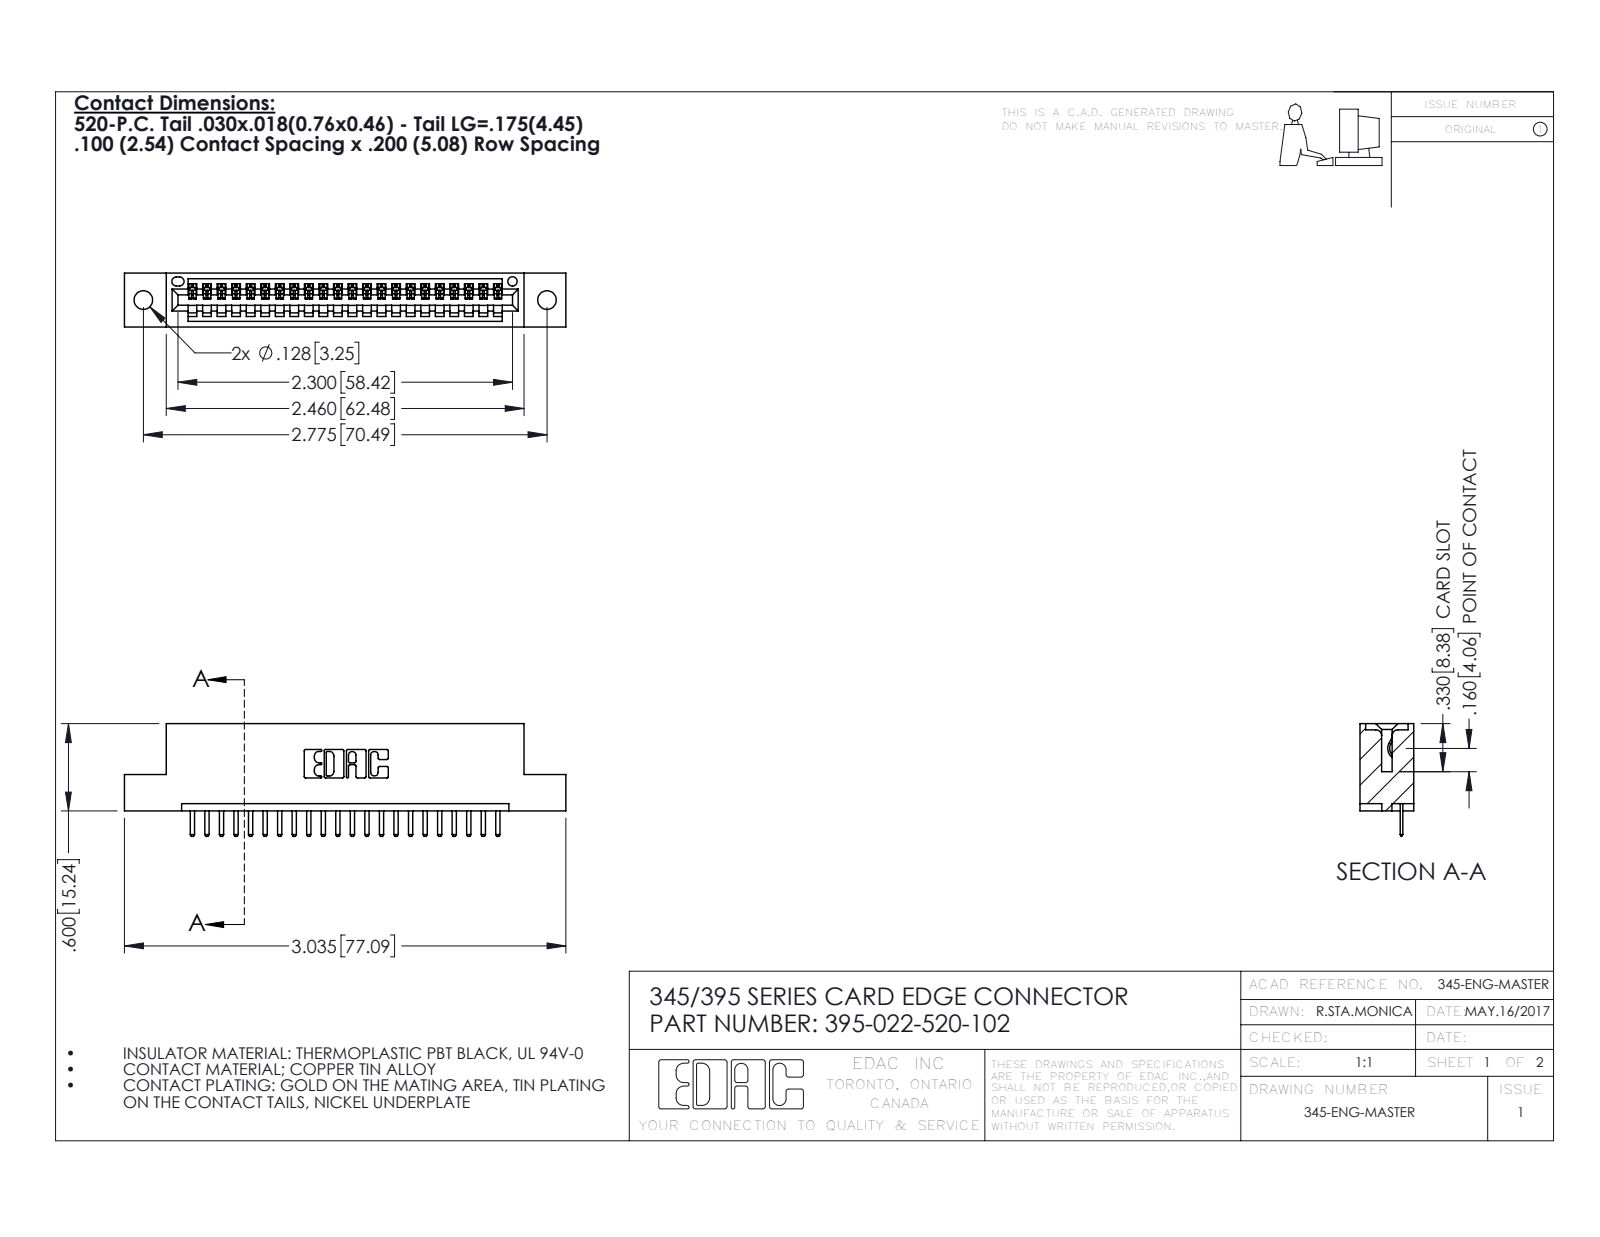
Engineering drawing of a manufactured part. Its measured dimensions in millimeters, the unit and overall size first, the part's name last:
Units: millimetres
Overall size (bounding box): 77.1 × 19.7 × 9.4
Round holes (diameter × count): ⌀3.3 ×2, ⌀1.6 ×1
Partial cylindrical surfaces — rounded edges, fillets, slot ends (radius × count): R0.3 ×46, R0.2 ×44, R0.3 ×22, R0.2 ×6, R0.8 ×6, R0.7 ×3, R0.8 ×2, R1 ×2
Main face-to-face distances: 7.6, 1.8, 9.4, 5.1, 2.5, 6.9, 0.6, 5.7, 1.8, 3.8
Hole centre spacings: 6.9, 64.5, 70.5
Volume: 7 060 mm³ · Surface area: 8 632 mm²
Bodies: 23 solids, 1490 faces (1004 planar, 486 cylindrical, 0 other)
Part name (STEP PRODUCT): 395-022-520-102; 345-292-001_345-293-120; 345 Part_Flush Mounting Lugs - 0.128 Dia
STEP written by: SolidWorks 2016 (CONFIG_CONTROL_DESIGN)
